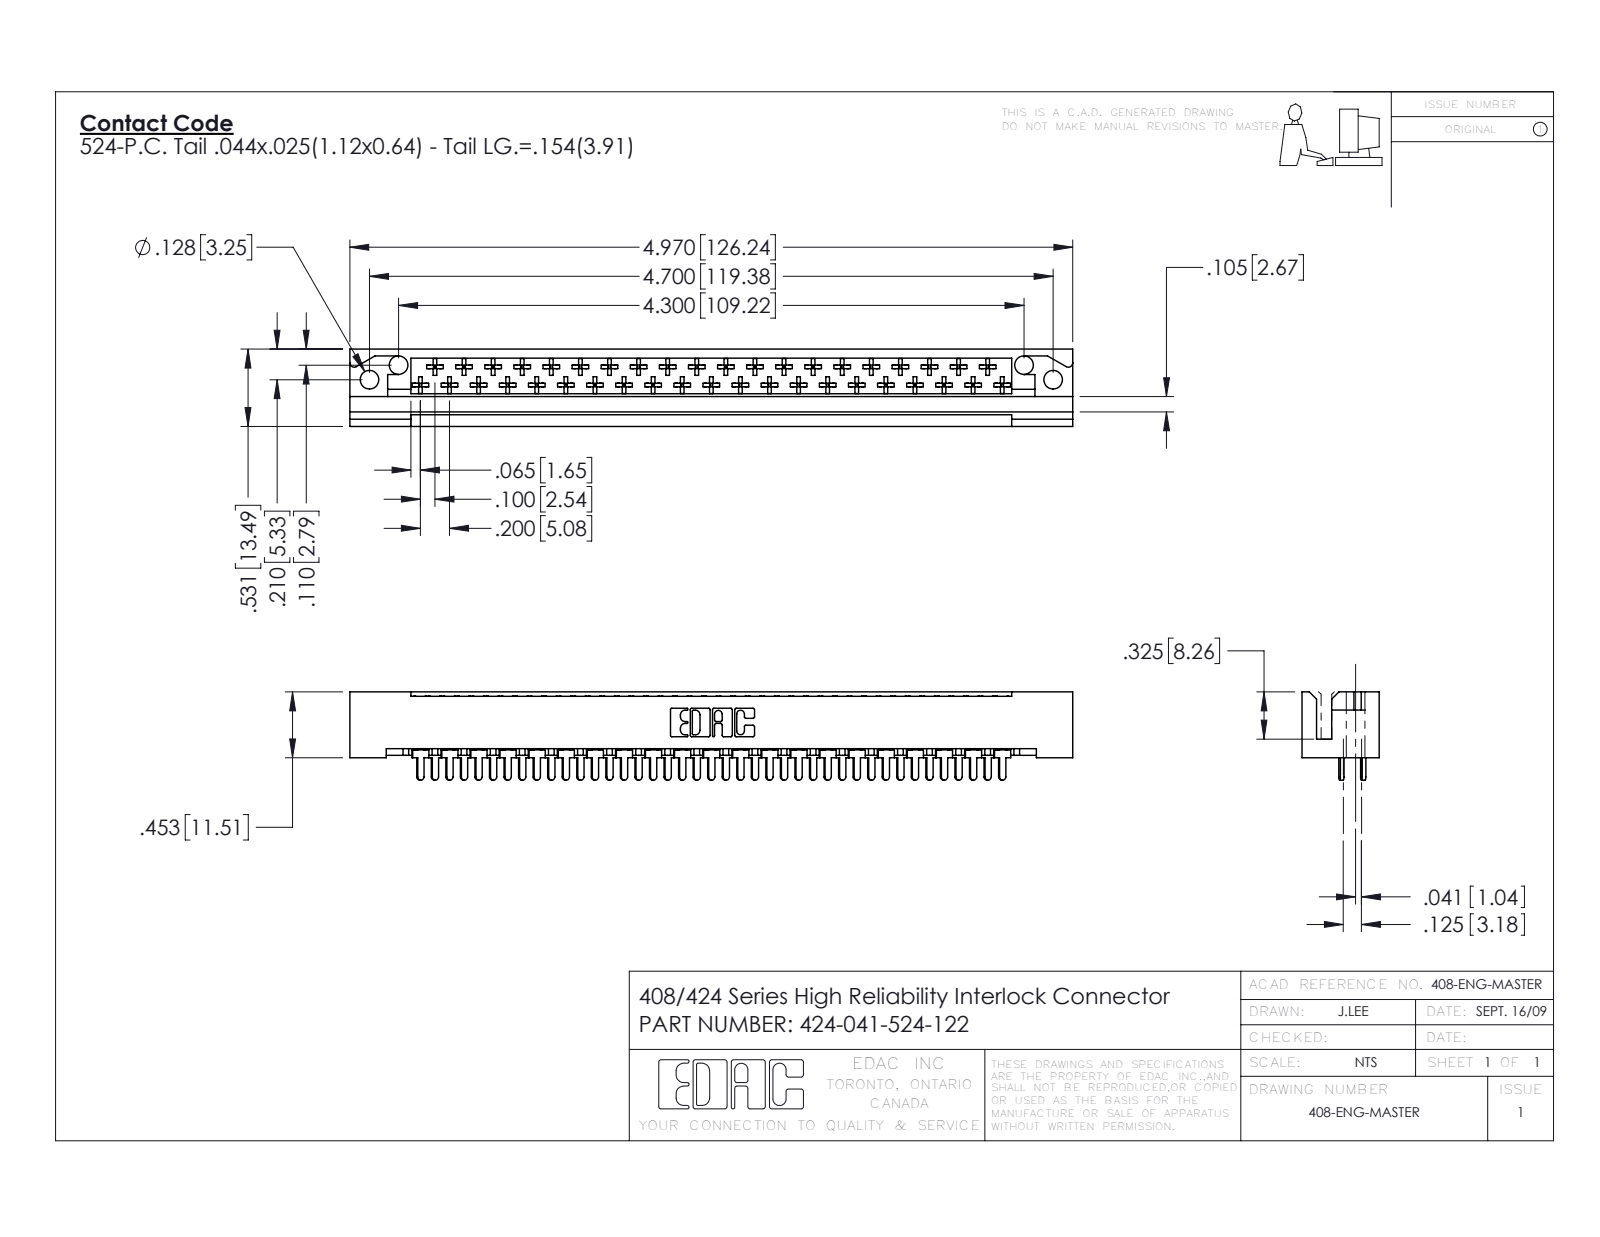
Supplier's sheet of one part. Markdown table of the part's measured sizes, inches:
| quantity | value |
| --- | --- |
| part name | 424-041-524-122; 408-290-001_408-290-124 - Bottom; 424 Part_041; 408-290-001_408-290-124 - Top |
| STEP written by | SolidWorks 2016 (CONFIG_CONTROL_DESIGN) |
| units | inches |
| bodies | 42 solids, 2400 faces (1811 planar, 425 cylindrical, 164 other) |
| overall size | 4.97 × 0.607 × 0.531 |
| volume | 0.798 in³ |
| surface area | 26.7 in² |
| round holes (diameter × count) | 0.128 × 4 |
| partial cylindrical surfaces (radius × count) | 0.01 × 246, 0.02 × 43, 0.022 × 41, 0.01 × 22, 0.007 × 6, 0.031 × 6, 0.026 × 3, 0.03 × 2 |
| main face-to-face distances | 0.1, 0.296, 0.025, 0.531, 0.125, 0.272, 0.235, 0.259, 0.025, 0.217 |
| hole center spacings | 0.224, 4.501, 4.3, 4.7 |
